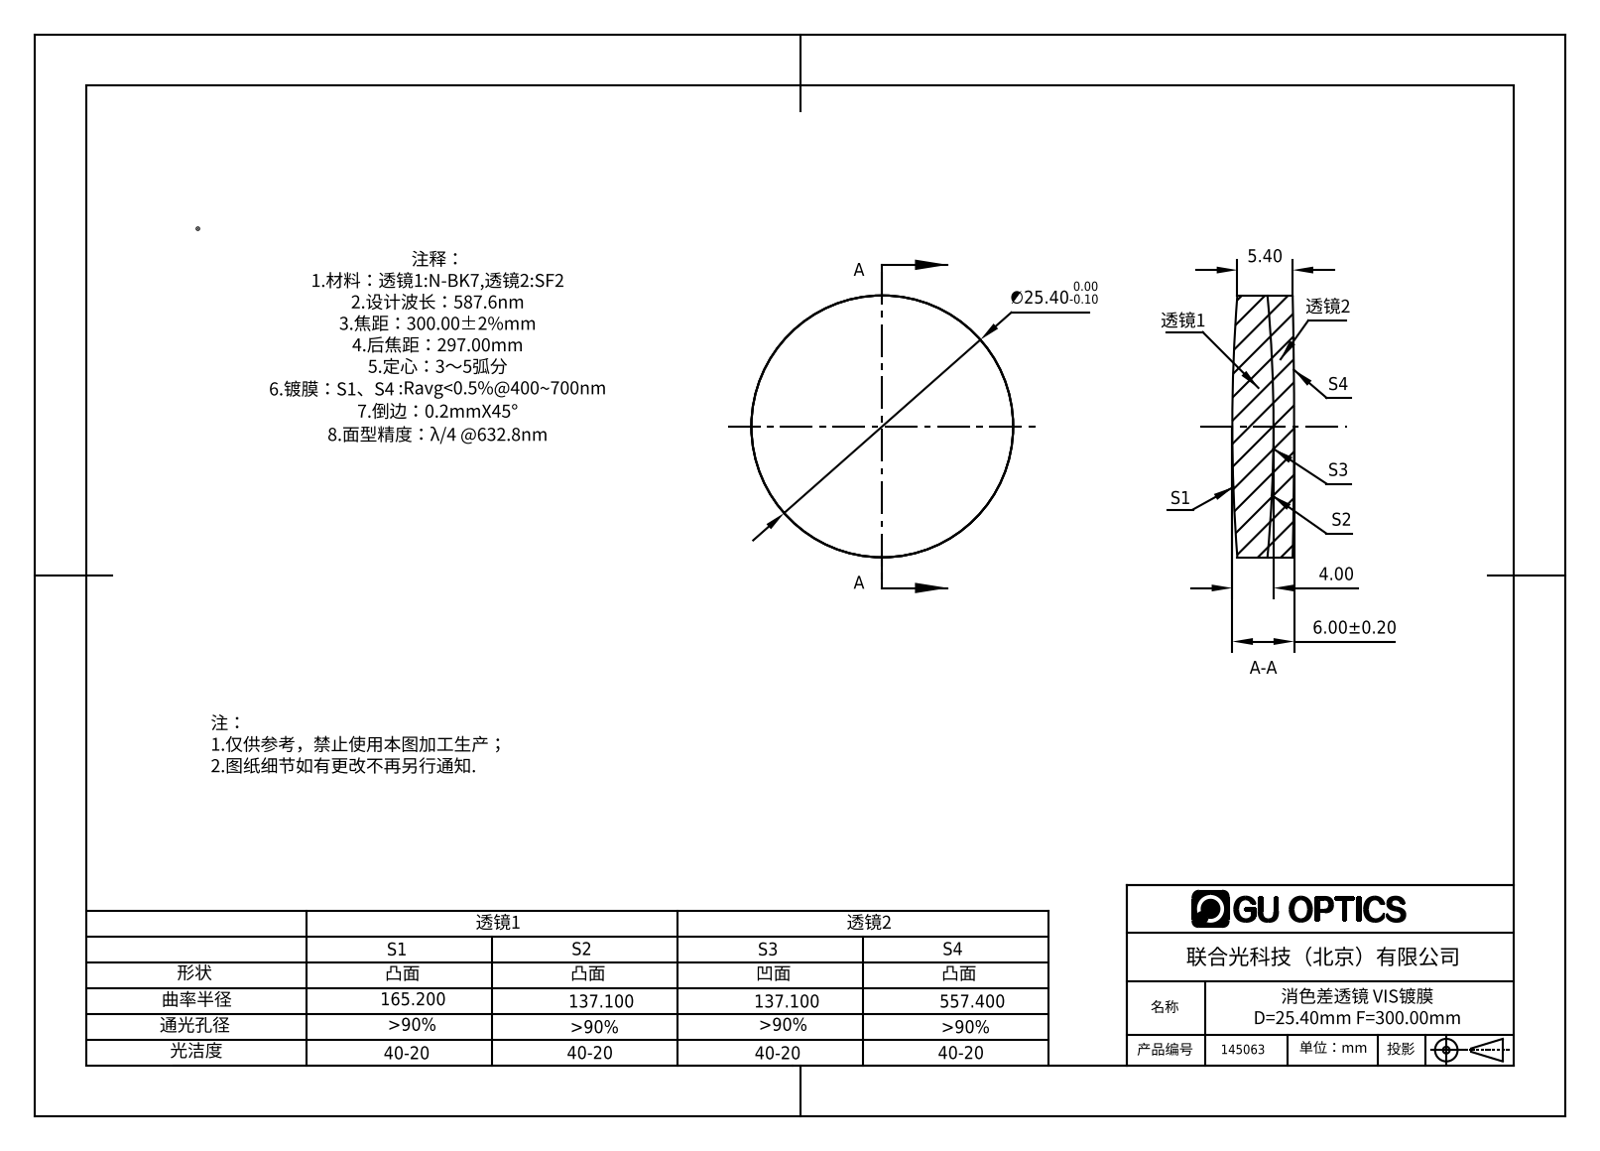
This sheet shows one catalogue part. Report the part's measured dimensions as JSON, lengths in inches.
{"part_name": "145063", "step_written_by": "SolidWorks 2016 (AUTOMOTIVE_DESIGN)", "units": "inches", "bodies": {"solids": 2, "faces": 12, "planar": 0, "cylindrical": 4, "other": 8}, "overall_size": [1, 1, 0.236], "volume_in3": 0.176, "surface_area_in2": 3.81, "round_bosses_or_shafts": [[1, 1]]}
